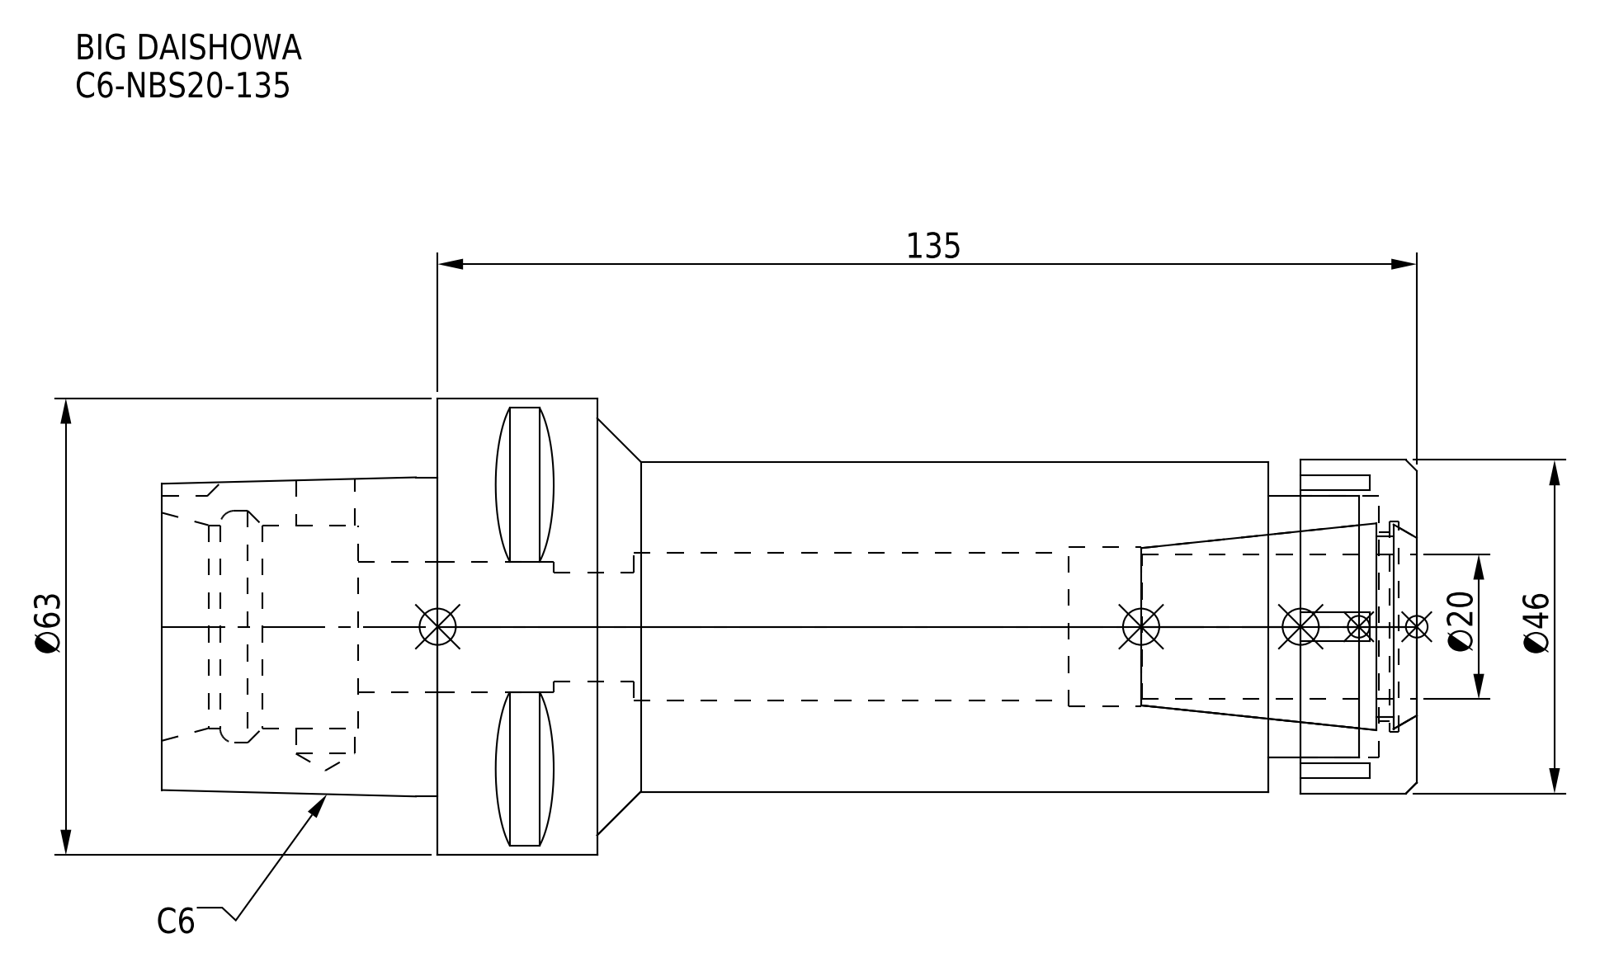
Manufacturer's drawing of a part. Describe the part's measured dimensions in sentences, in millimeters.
The part is named "NBN20_1.stp; C6-NBS20-135.stp; DXF_TEMP_ASSY_ASM_4_ASM.stp; C6-NBS20-135-200_ASM.stp (+3 more)". Its 3-D file was written by "SolidWorks 2019 (CONFIG_CONTROL_DESIGN)". It is 2 solids with 112 faces: 61 planar, 33 cylindrical and 18 other. Overall it measures 173 by 63 by 63 millimeters. Its volume is 234 570 cubic millimeters and its surface area 47 859 square millimeters. Round holes: 1 of diameter 8.1, 1 of diameter 15, 1 of diameter 18, 1 of diameter 20.3, 1 of diameter 22, 1 of diameter 26, 1 of diameter 28, 1 of diameter 29, 1 of diameter 32, 1 of diameter 36. Round bosses or shafts: 1 of diameter 63, 1 of diameter 46, 1 of diameter 45.5. Partial cylindrical surfaces (rounded edges, fillets, slot ends): 1 of radius 5. The main face-to-face distances are 135, 8, 38, 16, 119, 20.5, 114.5, 27, 4.5, 60.
